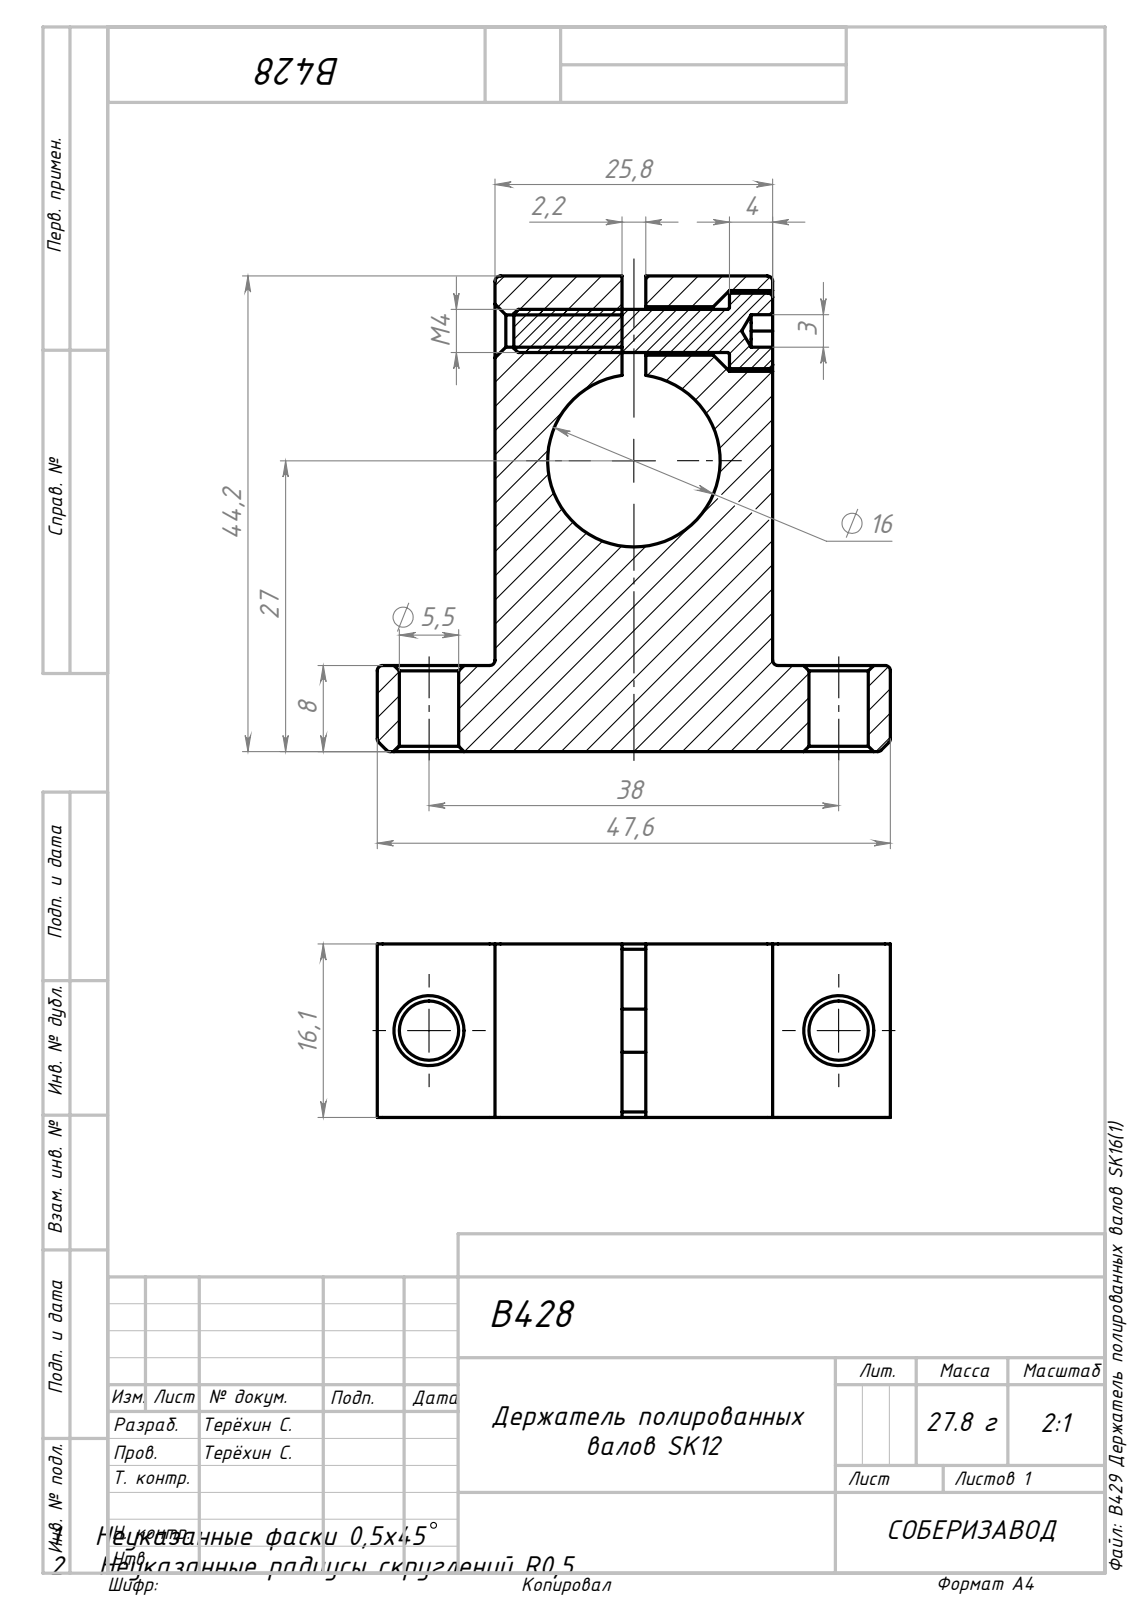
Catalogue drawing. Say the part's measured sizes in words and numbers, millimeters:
The part is named "Сборка12; socket head cap screw_din_DIN 912 M4 x 20 --- 20N; B429 Держатель полированных валов SK16_00". Its 3-D file was written by "SolidWorks 2024 (AUTOMOTIVE_DESIGN)". It is 2 solids with 83 faces: 30 planar, 27 cylindrical and 26 other. Overall it measures 47.6 by 44.15 by 16.1 millimeters. Its volume is 17 113 cubic millimeters and its surface area 6 948 square millimeters. Round holes: 2 of diameter 5.5, 1 of diameter 3, 1 of diameter 4.5, 1 of diameter 7.5, 1 of diameter 16. Round bosses or shafts: 1 of diameter 7, 1 of diameter 4. Partial cylindrical surfaces (rounded edges, fillets, slot ends): 10 of radius 0.5. The main face-to-face distances are 16.1, 25.75, 44.15, 8, 36.15, 22.7, 24.9, 11.78, 13.97, 13.98. The hole center spacings are 38.
